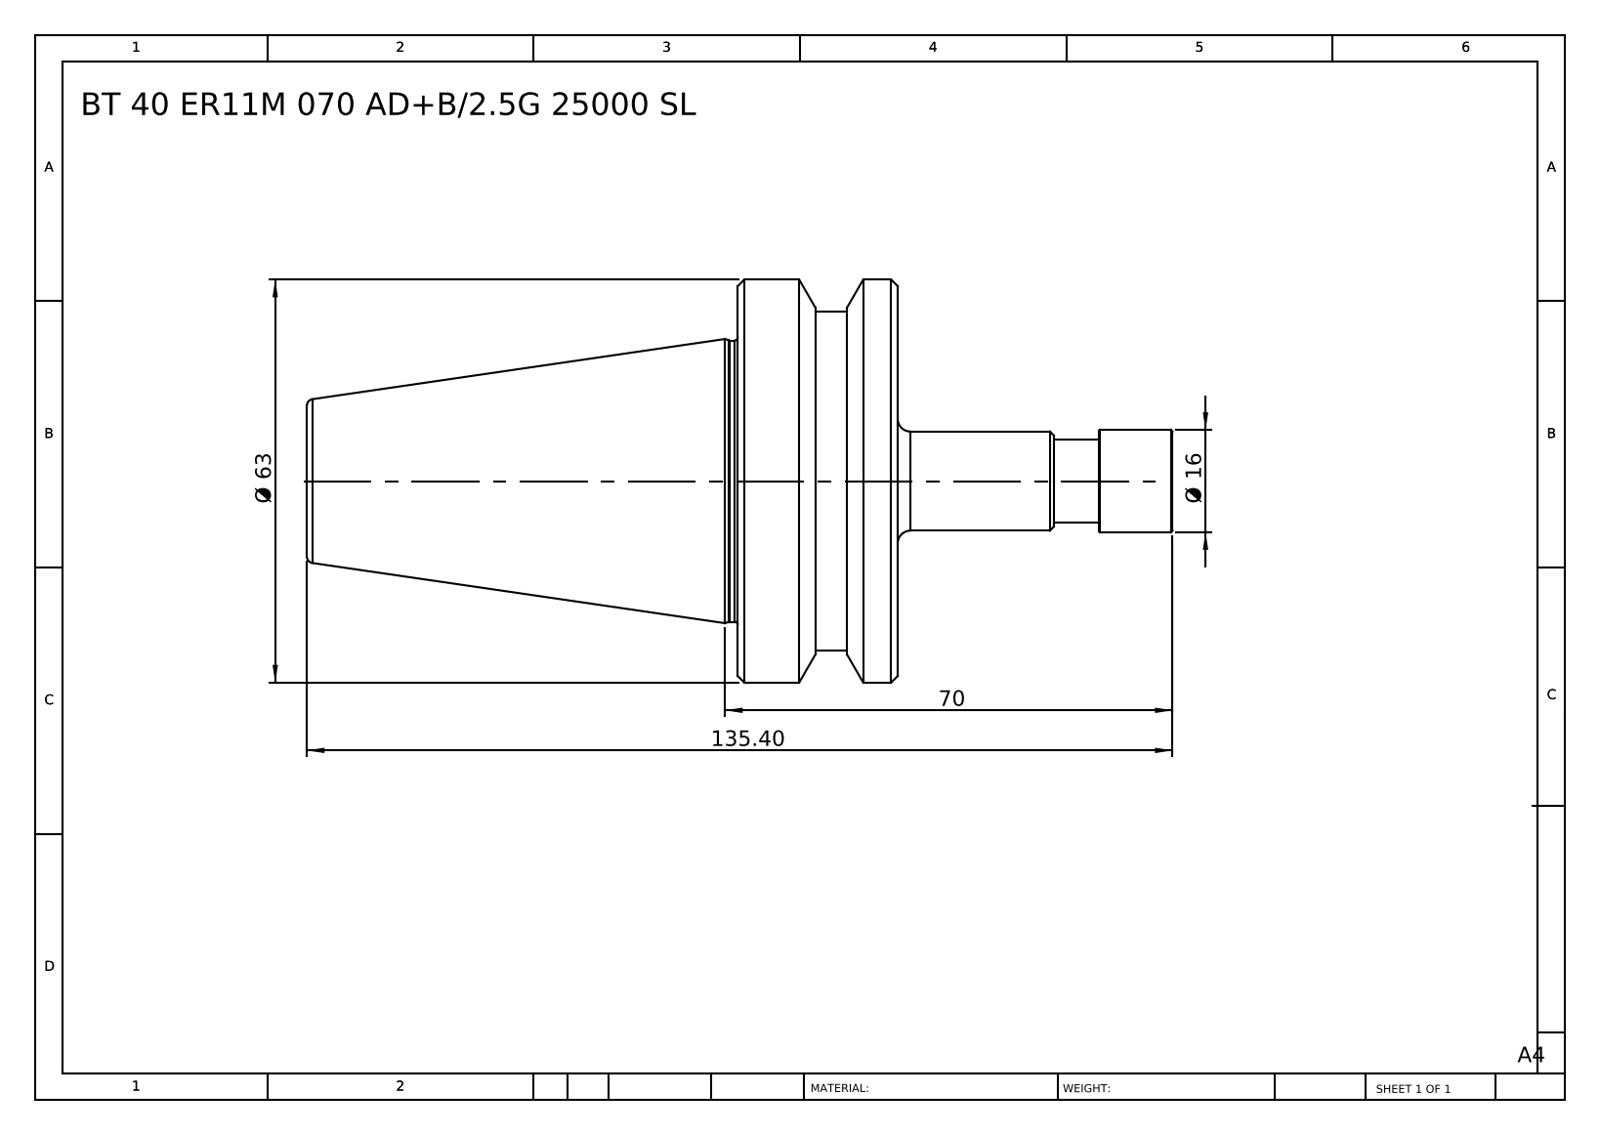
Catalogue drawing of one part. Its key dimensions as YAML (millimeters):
part_name: "BT 40 ER11M 070 AD+B-2.5G 25000 SL"
step_written_by: "SolidWorks 2014 (CONFIG_CONTROL_DESIGN)"
units: millimeters
bodies: {solids: 1, faces: 48, planar: 8, cylindrical: 14, other: 26}
overall_size: [135.4, 63, 63]
volume: 146224
surface_area: 20457
round_bosses_or_shafts:
  - {diameter: 63, count: 1}
  - {diameter: 53, count: 1}
  - {diameter: 44, count: 1}
  - {diameter: 16, count: 1}
  - {diameter: 15.5, count: 1}
  - {diameter: 12.9, count: 1}
face_to_face_distances: [25, 92.4, 67.4, 43, 68, 135.4, 50.9, 55.9, 7.9, 12.9]
